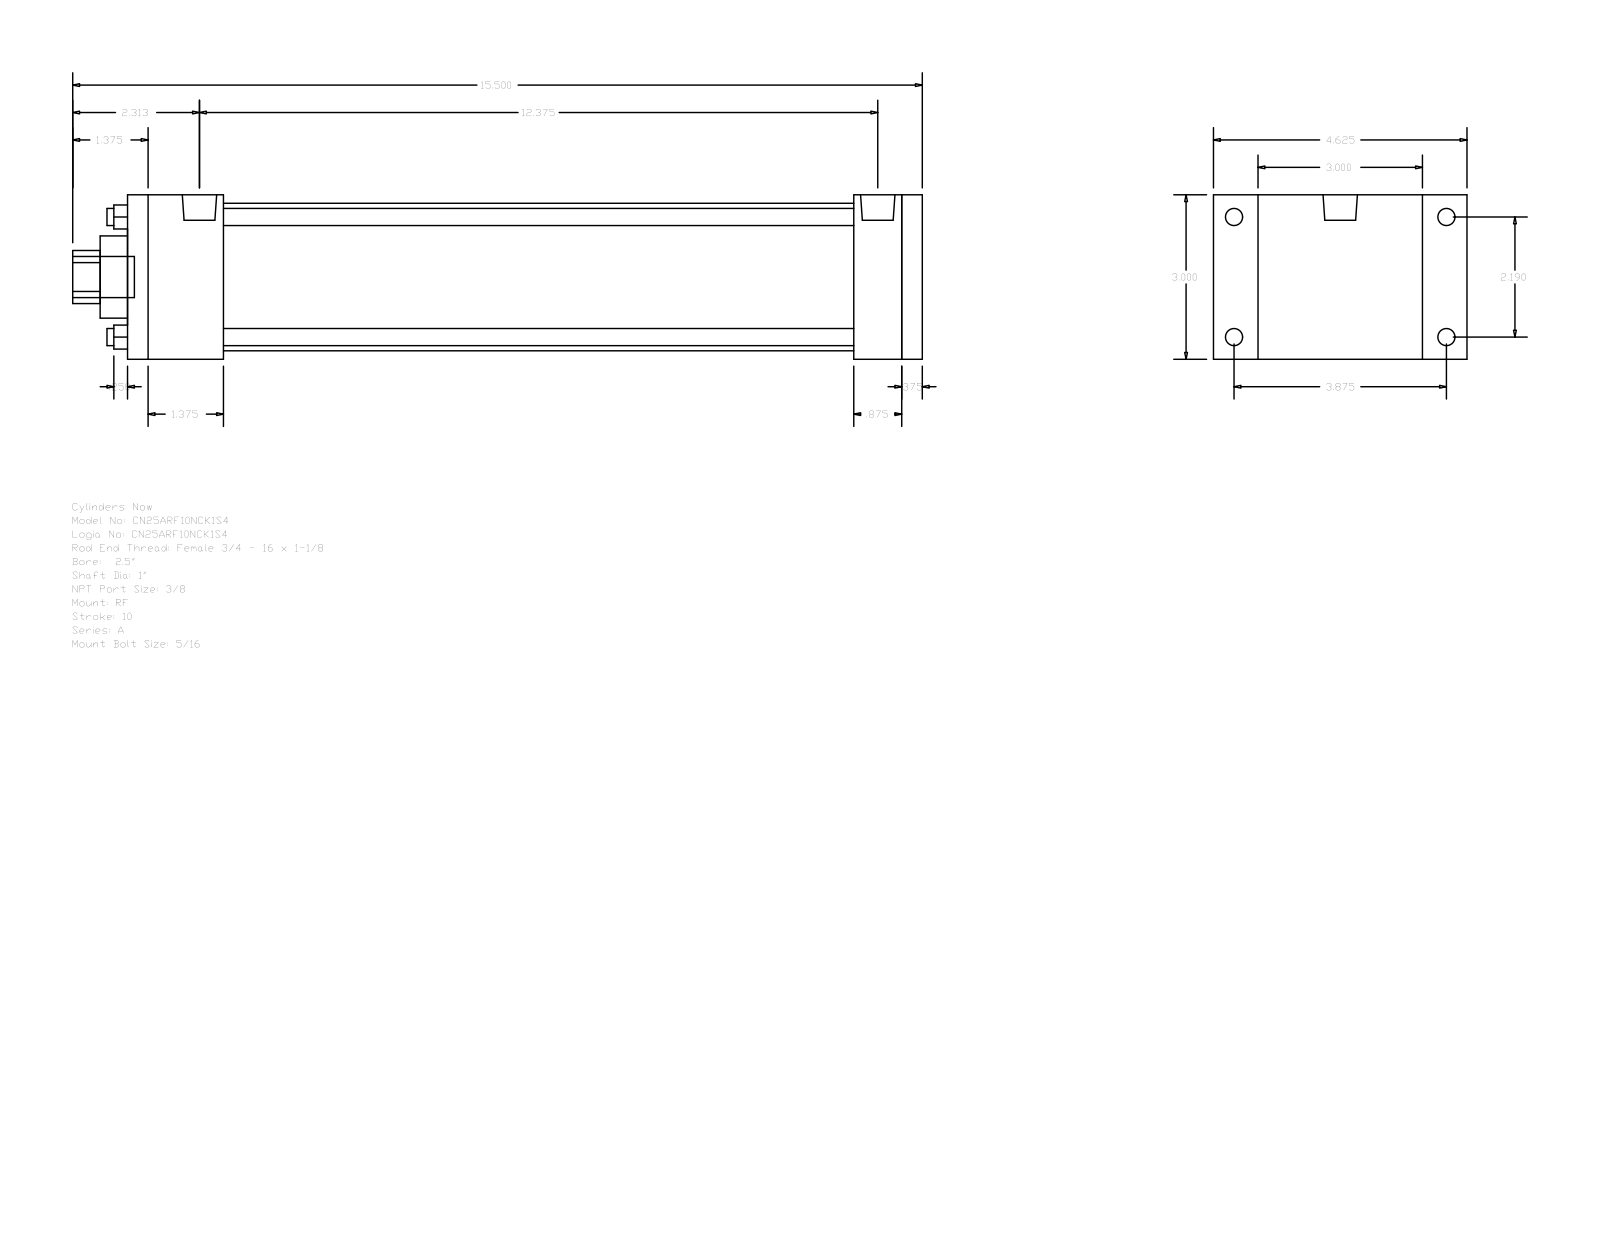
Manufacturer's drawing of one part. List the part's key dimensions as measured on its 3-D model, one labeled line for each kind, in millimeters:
Part name (STEP PRODUCT): A_RF__0250_1
STEP written by: GSSL Pune (CONFIG_CONTROL_DESIGN)
Units: millimetres
Bodies: 0 solids, 92 faces (64 planar, 28 cylindrical, 0 other)
Overall size (bounding box): 393.7 × 117.47 × 76.2
Round holes (diameter × count): ⌀7.94 ×4, ⌀25.4 ×1, ⌀38.1 ×1, ⌀68.33 ×1
Round bosses / shafts (diameter × count): ⌀7.94 ×4, ⌀5.56 ×4, ⌀15.93 ×2, ⌀19.05 ×1
Partial cylindrical surfaces — rounded edges, fillets, slot ends (radius × count): R12.29 ×1
Main face-to-face distances: 76.2, 368.3, 9.52, 358.78, 44.45, 336.55, 292.1, 314.33, 323.85, 22.23
Hole centre spacings: 39.33, 55.62, 78.66
